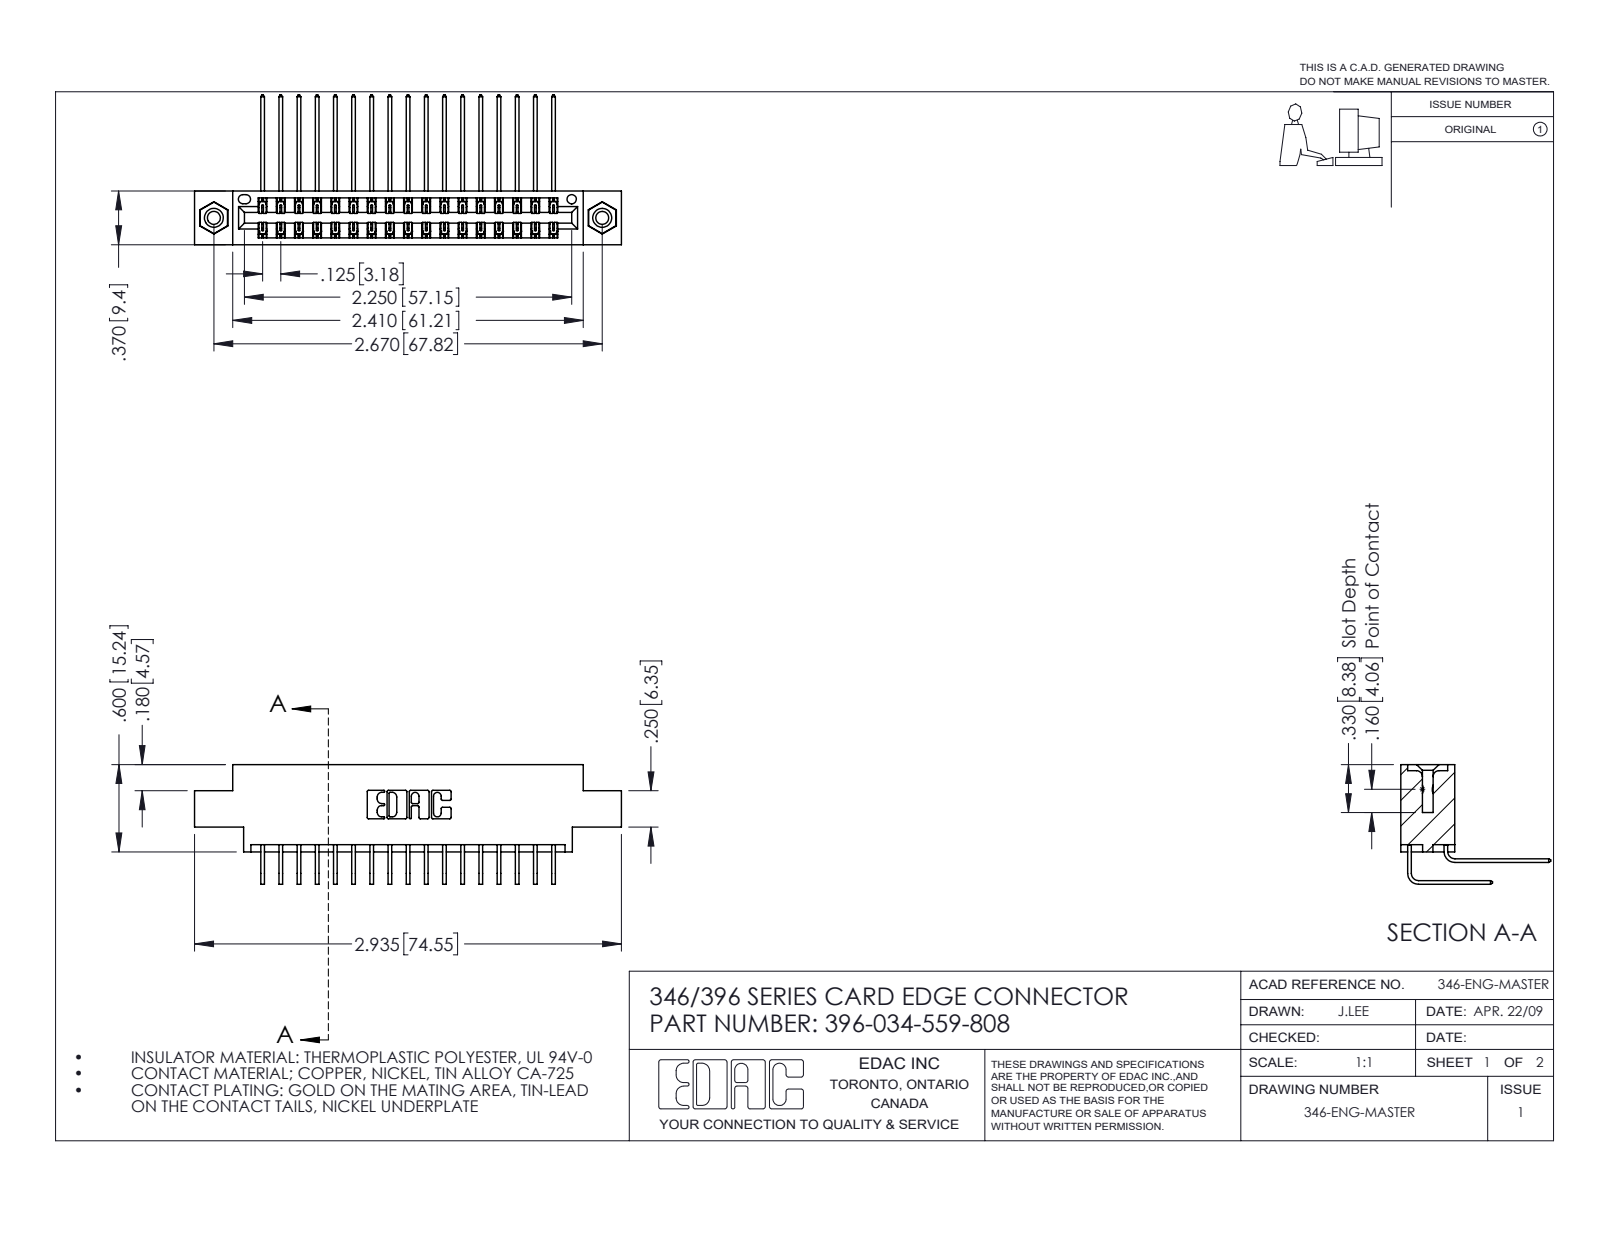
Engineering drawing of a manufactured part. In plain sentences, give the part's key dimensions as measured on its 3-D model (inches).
The part is named "396-034-559-808; 346 Part_0.170 Offset - 0.156 Dia-TI; 345-292-001_559 Tail - 2; 345-250-001_345-250-003-102 (+1 more)". Its 3-D file was written by "SolidWorks 2016 (CONFIG_CONTROL_DESIGN)". It is 37 solids with 2022 faces: 1370 planar, 636 cylindrical and 16 other. Overall it measures 2.935 by 1.03 by 0.823 inches. Its volume is 0.434 cubic inches and its surface area 16.31 square inches. Round holes: 2 of diameter 0.089, 2 of diameter 0.125, 2 of diameter 0.156, 1 of diameter 0.064. Round bosses or shafts: 2 of diameter 0.155. Partial cylindrical surfaces (rounded edges, fillets, slot ends): 51 of radius 0.006, 22 of radius 0.01, 6 of radius 0.007, 6 of radius 0.031, 3 of radius 0.026, 2 of radius 0.014, 2 of radius 0.022, 2 of radius 0.024. The main face-to-face distances are 0.048, 0.322, 0.37, 0.25, 0.025, 0.072, 0.298, 0.275, 0.222, 0.148. The hole center spacings are 0.246, 2.463, 2.67.
